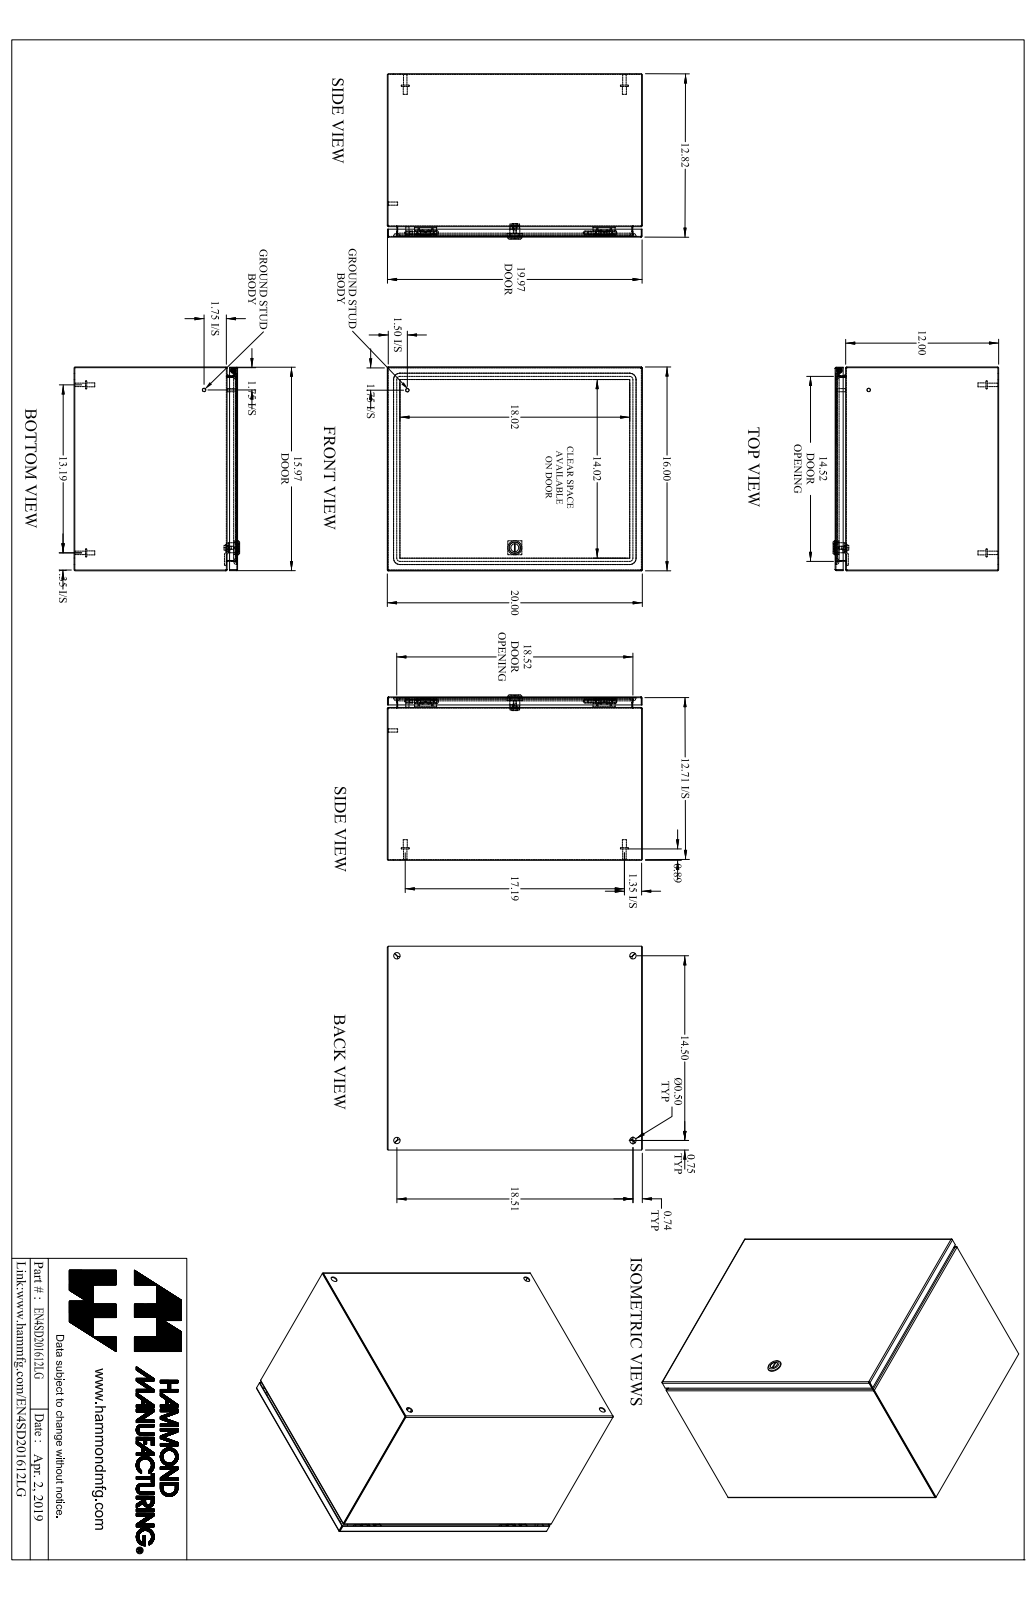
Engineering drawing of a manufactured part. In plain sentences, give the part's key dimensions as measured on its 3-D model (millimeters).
The part is named "EN4SD201612LG_Default". Its 3-D file was written by "SolidWorks 2019 (CONFIG_CONTROL_DESIGN)". It is 23 solids with 622 faces: 293 planar, 201 cylindrical and 128 other. Overall it measures 508 by 406.4 by 329.7 millimeters. Its volume is 1 650 000 cubic millimeters and its surface area 2 225 000 square millimeters. Round holes: 4 of diameter 12.7, 1 of diameter 4.4, 1 of diameter 5.9, 1 of diameter 6.1, 1 of diameter 6.1, 1 of diameter 15.9, 1 of diameter 19.9. Round bosses or shafts: 4 of diameter 15.9, 4 of diameter 8, 4 of diameter 6.9, 2 of diameter 7.1, 2 of diameter 6.4, 1 of diameter 27.9, 1 of diameter 13.3, 1 of diameter 11.6. Partial cylindrical surfaces (rounded edges, fillets, slot ends): 19 of radius 0.7, 19 of radius 2.2, 12 of radius 4.8, 4 of radius 0.2, 4 of radius 1.6, 4 of radius 6.4, 4 of radius 12.7, 2 of radius 3.2. The main face-to-face distances are 1.4, 324.2, 405, 506.6, 322.8, 325.7, 403.5, 406.4, 505.1, 508. The hole center spacings are 368.3, 470.3, 597.3, 236.4, 236.9, 414.5, 414.7.
